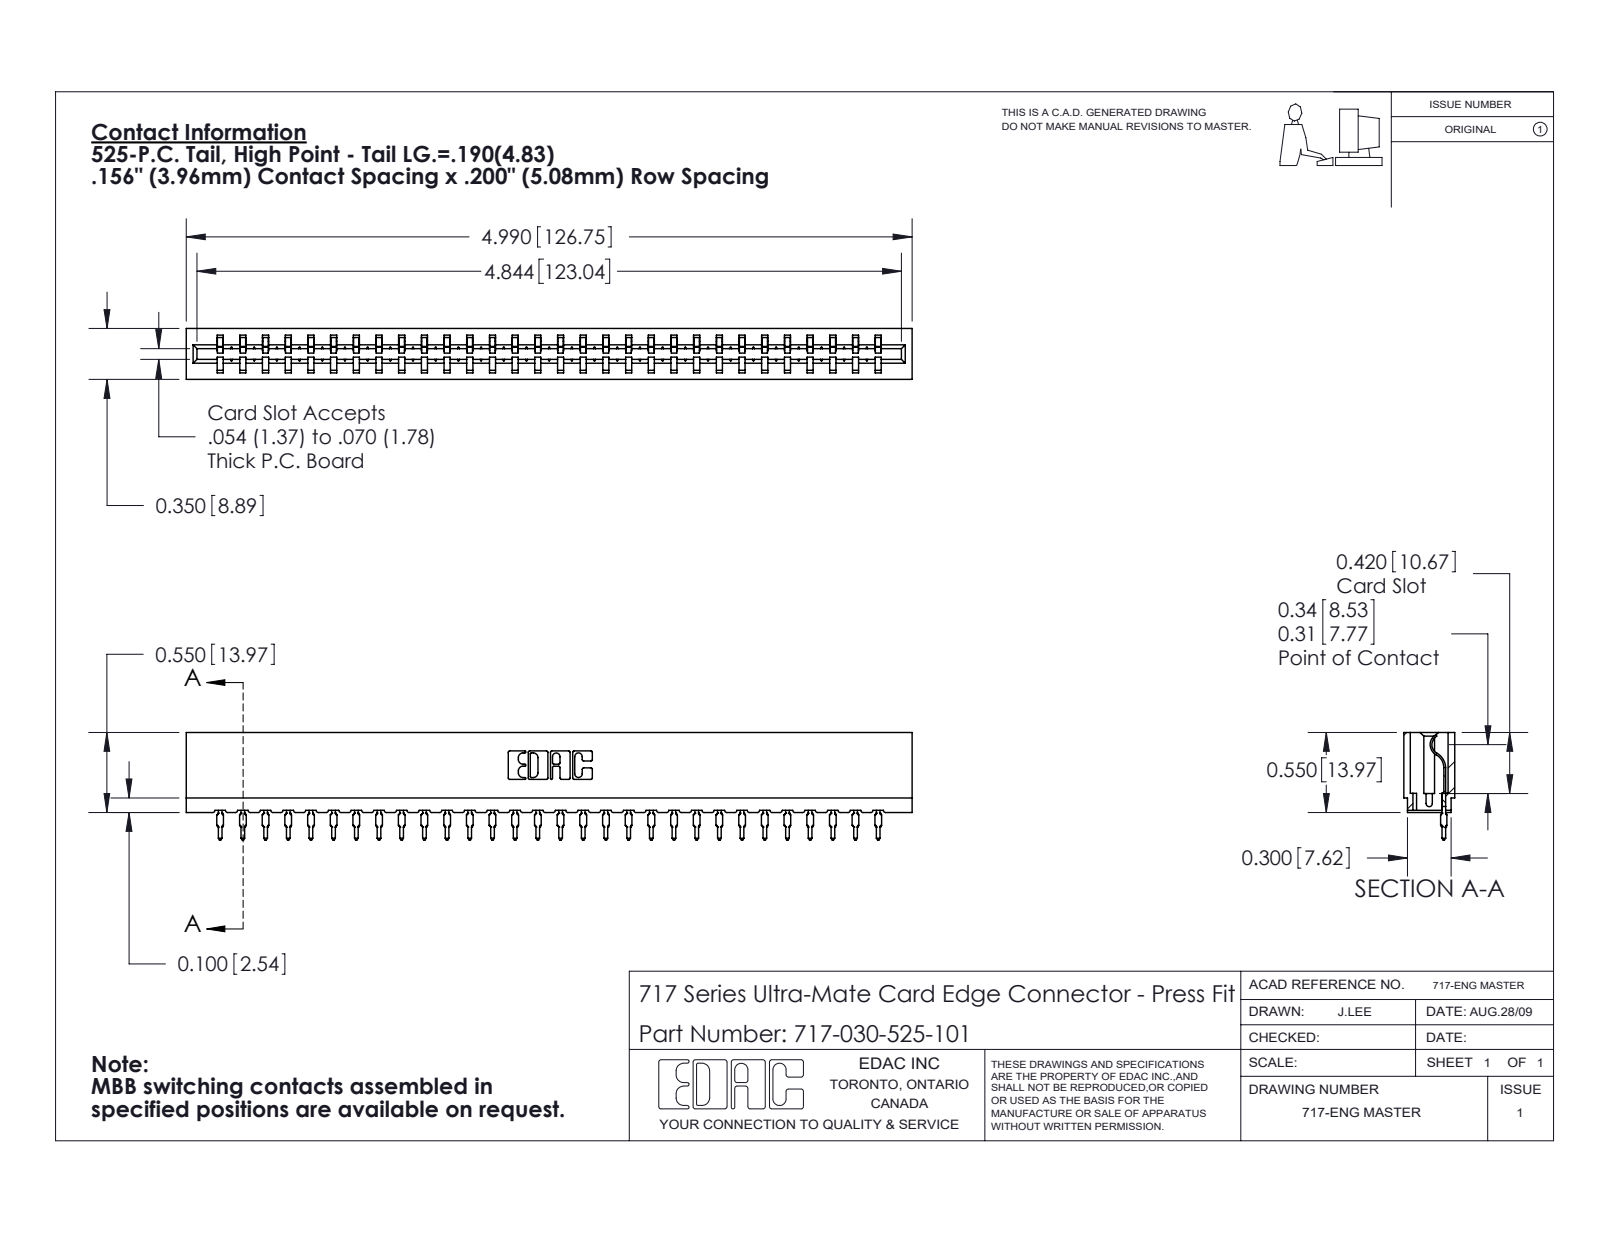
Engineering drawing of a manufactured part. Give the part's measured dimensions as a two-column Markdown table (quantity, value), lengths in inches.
| quantity | value |
| --- | --- |
| part name | 717 Part_Insulator Option - 06; 745-292-001_525; 717-030-525-101 |
| STEP written by | SolidWorks 2020 (CONFIG_CONTROL_DESIGN) |
| units | inches |
| bodies | 31 solids, 3484 faces (2094 planar, 610 cylindrical, 780 other) |
| overall size | 4.99 × 0.739 × 0.35 |
| volume | 0.655 in³ |
| surface area | 23.02 in² |
| partial cylindrical surfaces (radius × count) | 0.015 × 60, 0.021 × 60, 0.01 × 22, 0.007 × 6, 0.031 × 6, 0.005 × 4, 0.011 × 4, 0.026 × 3 |
| main face-to-face distances | 0.212, 0.138, 0.35, 0.074, 0.156, 0.045, 0.305, 0.093, 0.167, 0.025 |
